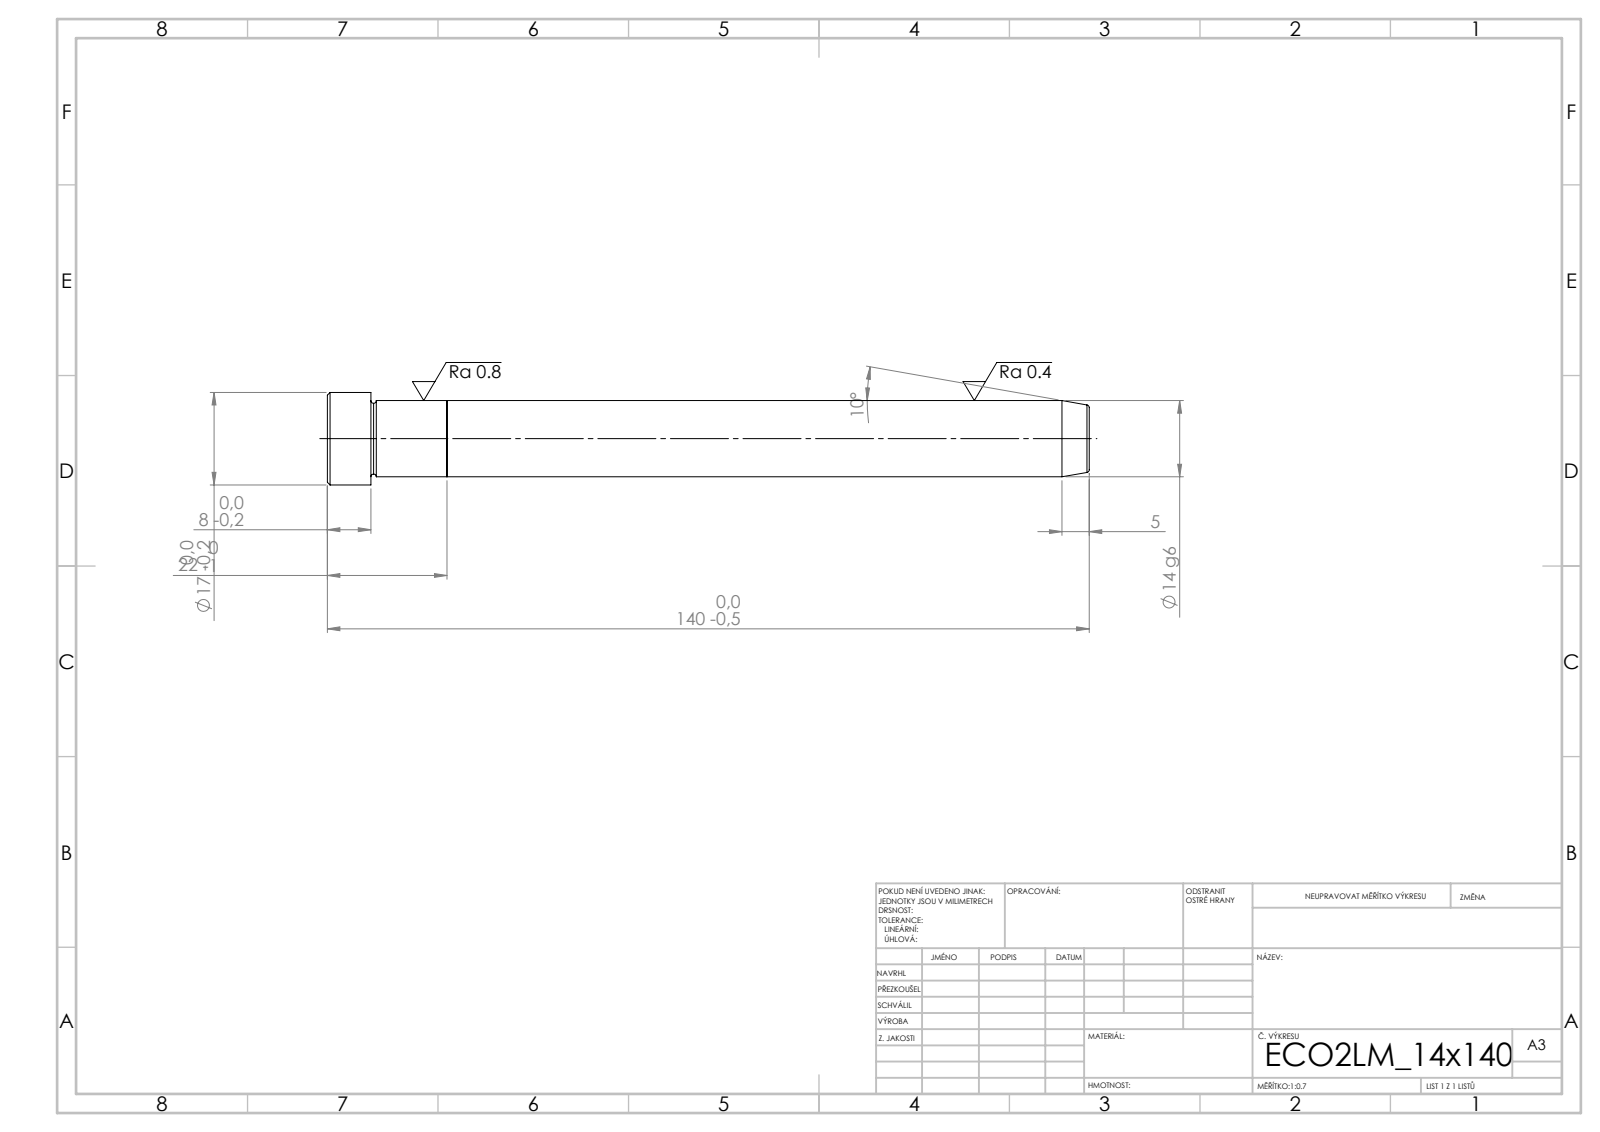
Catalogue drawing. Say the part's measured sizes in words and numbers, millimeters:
Its 3-D file was written by "SolidWorks 2019 (CONFIG_CONTROL_DESIGN)". It is 2 solids with 21 faces: 5 planar, 6 cylindrical and 10 other. Overall it measures 140 by 17 by 17 millimeters. Its volume is 22 018 cubic millimeters and its surface area 6 948 square millimeters. Round bosses or shafts: 1 of diameter 17, 1 of diameter 14. The main face-to-face distances are 22, 118, 140, 132, 14, 8.
